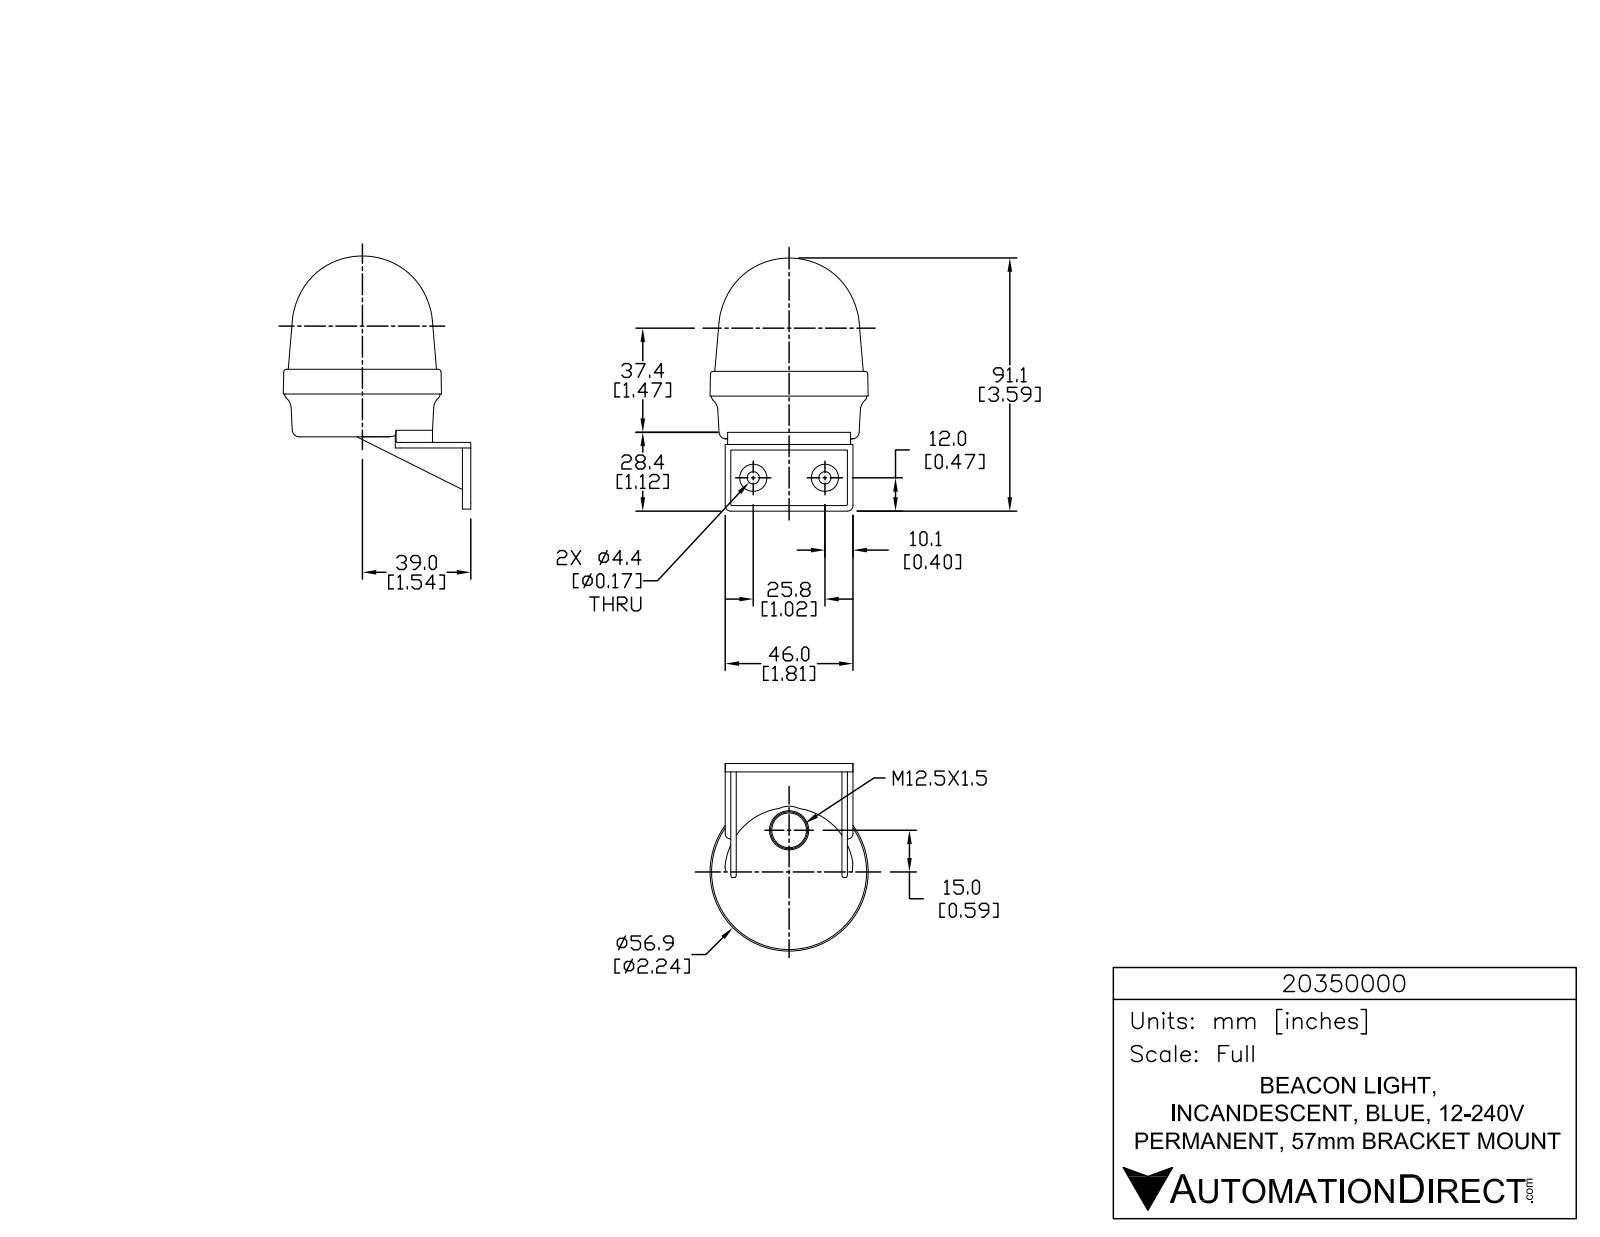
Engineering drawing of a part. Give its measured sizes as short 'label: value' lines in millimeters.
name: 20350000
written by: SolidWorks 2015 (AUTOMOTIVE_DESIGN)
unit: mm
bodies: 1 solid, 813 faces (550 planar, 169 cylindrical, 94 other)
size: 91.1 × 72.07 × 60.76
volume: 126 840 mm³; area: 18 525 mm²
holes: 3× ⌀0.99, 2× ⌀4.4
bosses: 3× ⌀5.74, 3× ⌀1.43, 2× ⌀9.8, 1× ⌀55.8
rounds: 6× R0.2, 6× R0.21, 6× R0.21, 6× R0.5, 6× R3.32, 4× R2, 3× R0.1, 3× R0.12
face distances: 2, 4, 40, 42, 1, 3, 38, 22, 24, 44.01
hole spacings: 25.8
